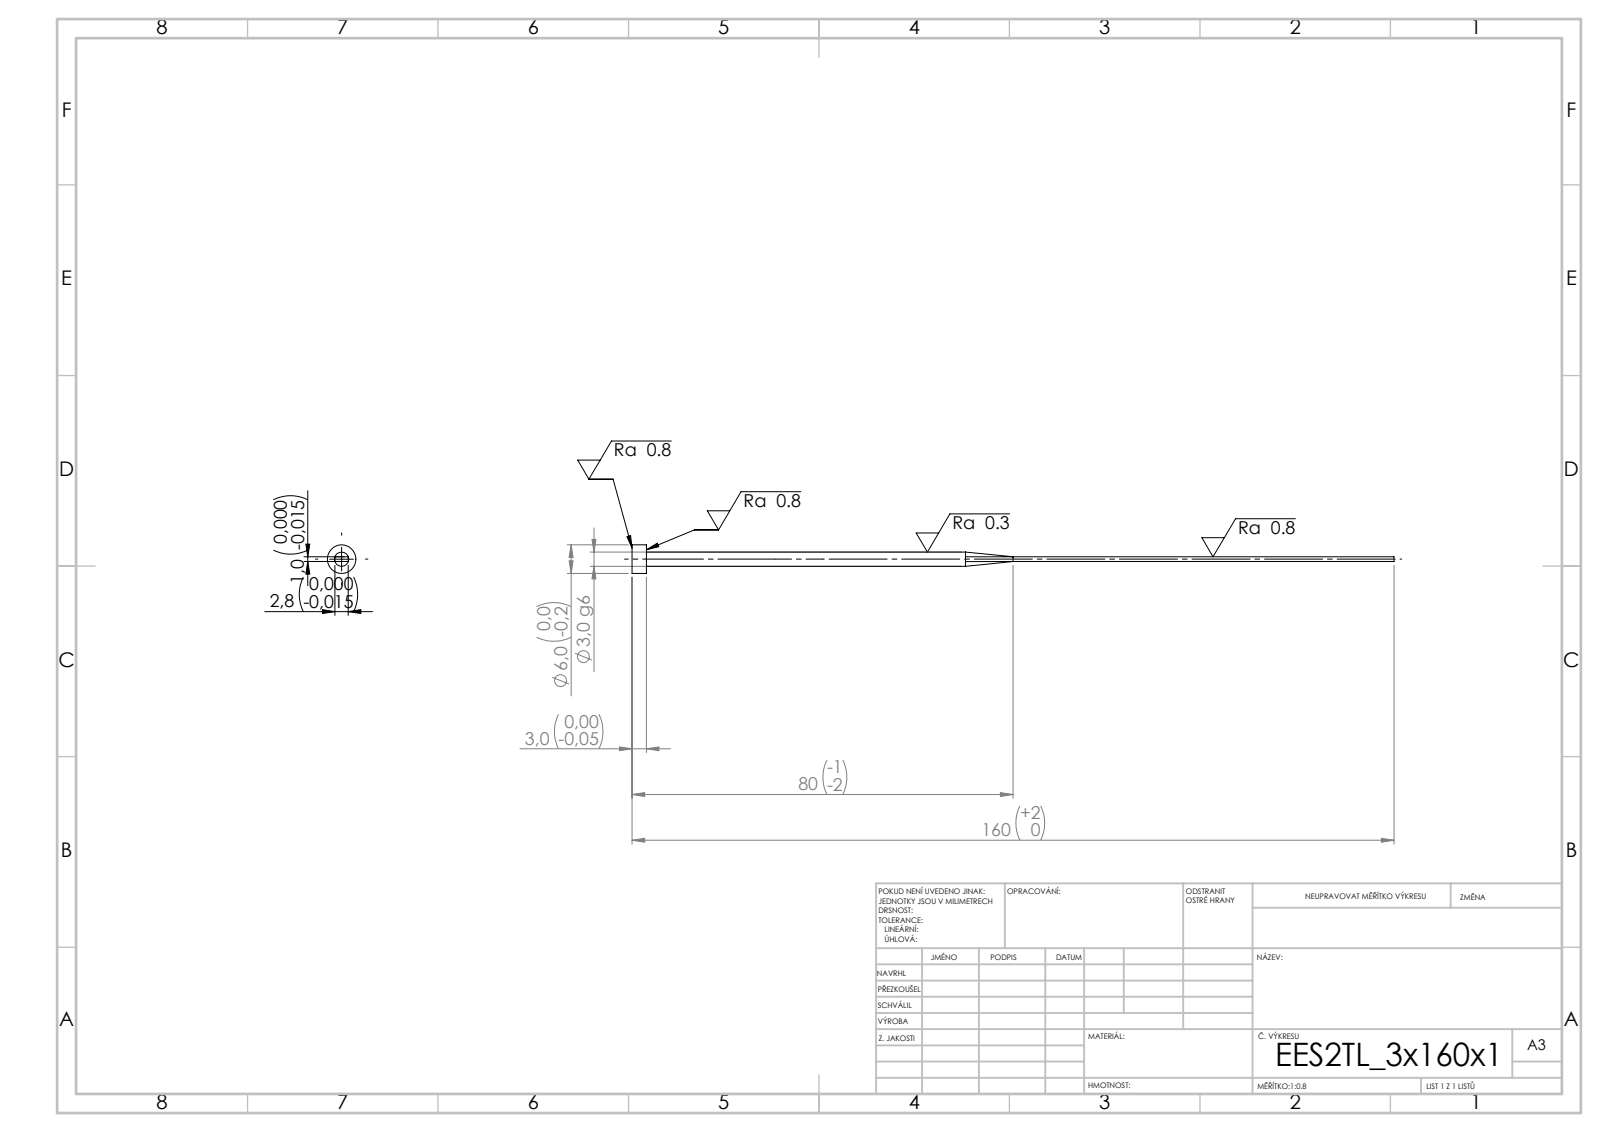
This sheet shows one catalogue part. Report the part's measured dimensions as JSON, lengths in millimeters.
{"step_written_by": "SolidWorks 2019 (CONFIG_CONTROL_DESIGN)", "units": "millimeters", "bodies": {"solids": 1, "faces": 15, "planar": 7, "cylindrical": 4, "other": 4}, "overall_size": [160, 6, 6], "volume_mm3": 831, "surface_area_mm2": 1431, "round_bosses_or_shafts": [[6, 1], [3, 1]], "face_to_face_distances": [1, 2.8, 3, 160, 157]}
